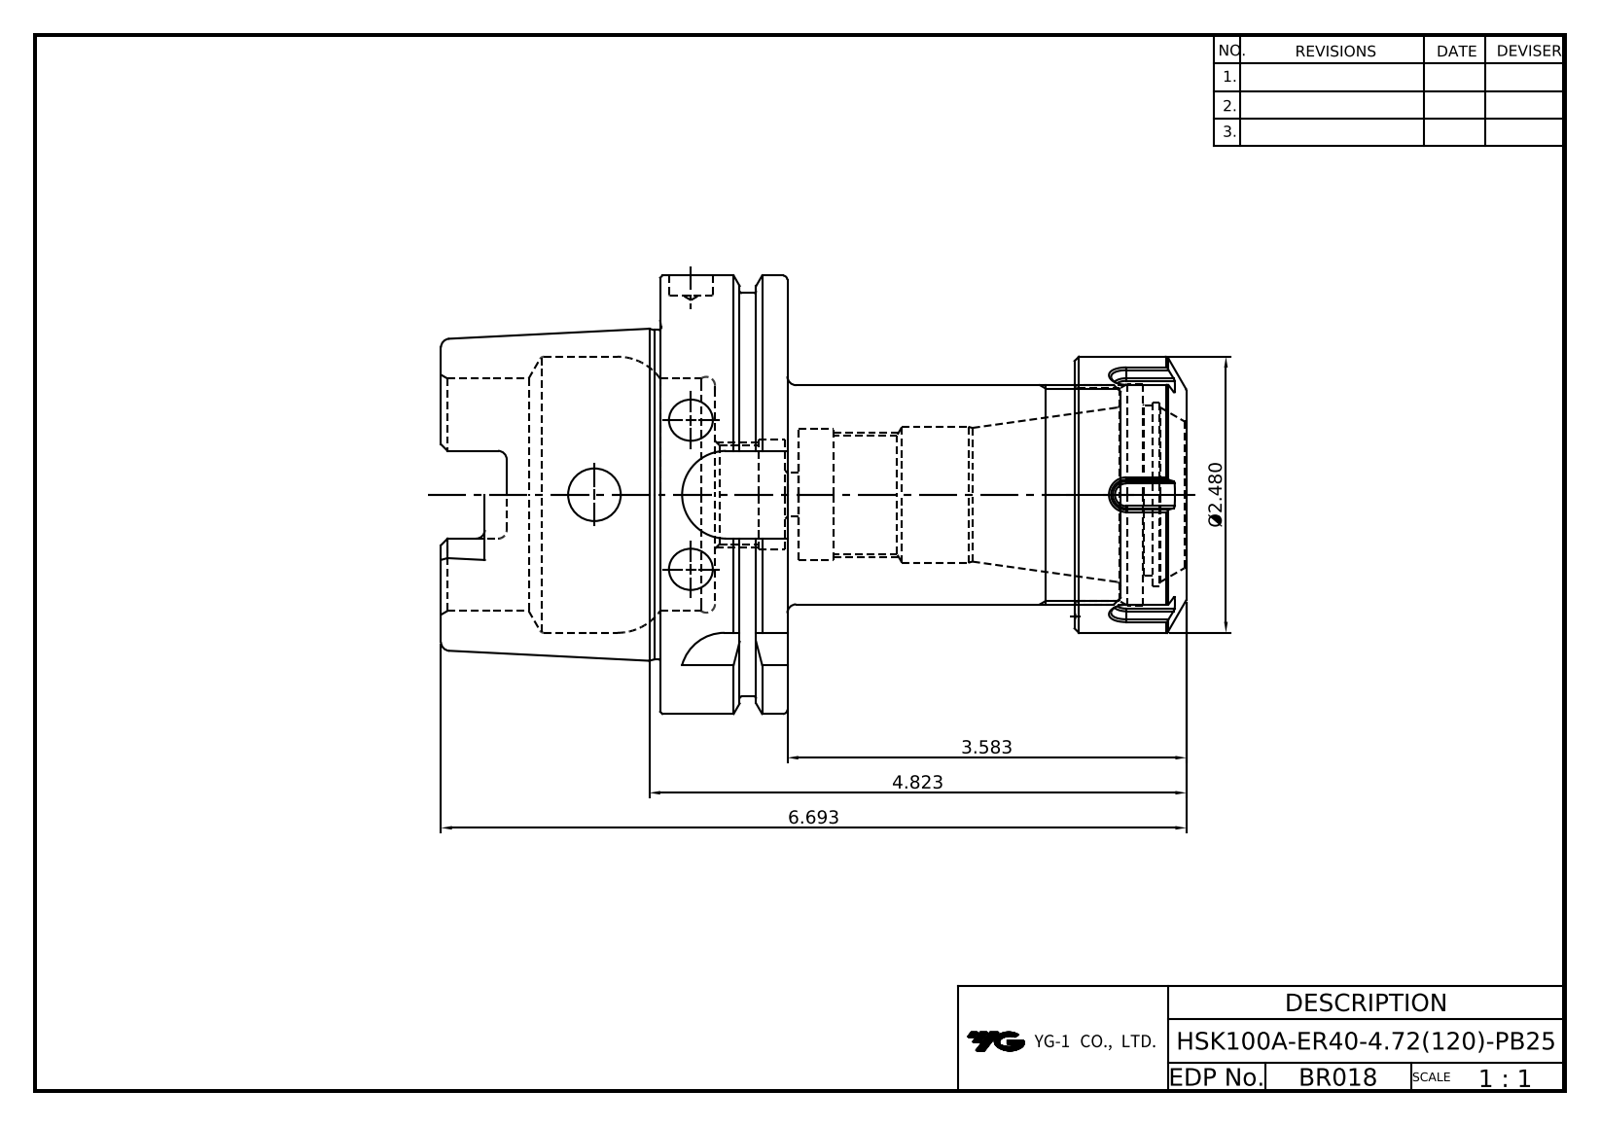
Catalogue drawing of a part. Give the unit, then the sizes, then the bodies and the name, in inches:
Units: inches
Overall size (bounding box): 6.693 × 3.937 × 3.937
Round holes (diameter × count): ⌀0.394 ×2, ⌀0.056 ×1, ⌀0.472 ×1, ⌀0.881 ×1, ⌀0.984 ×1, ⌀1.057 ×1, ⌀1.181 ×1, ⌀1.22 ×1, ⌀1.319 ×1, ⌀1.531 ×1, ⌀1.65 ×1, ⌀1.913 ×1
Round bosses / shafts (diameter × count): ⌀3.937 ×1, ⌀3.622 ×1, ⌀2.969 ×1, ⌀1.969 ×1
Partial cylindrical surfaces — rounded edges, fillets, slot ends (radius × count): R0.02 ×12, R0.079 ×6, R0.192 ×4, R0.394 ×4
Main face-to-face distances: 1.142, 0.492, 0.65, 1.969, 2.579, 2.461, 4.724, 4.232, 3.583, 3.72
Hole centre spacings: 1.093
Volume: 23.24 in³ · Surface area: 125.6 in²
Bodies: 2 solids, 201 faces (75 planar, 53 cylindrical, 73 other)
Part name (STEP PRODUCT): HSK100A-ER40-4.72; ER40NUT
STEP written by: Autodesk Inventor 2020 (AUTOMOTIVE_DESIGN)
